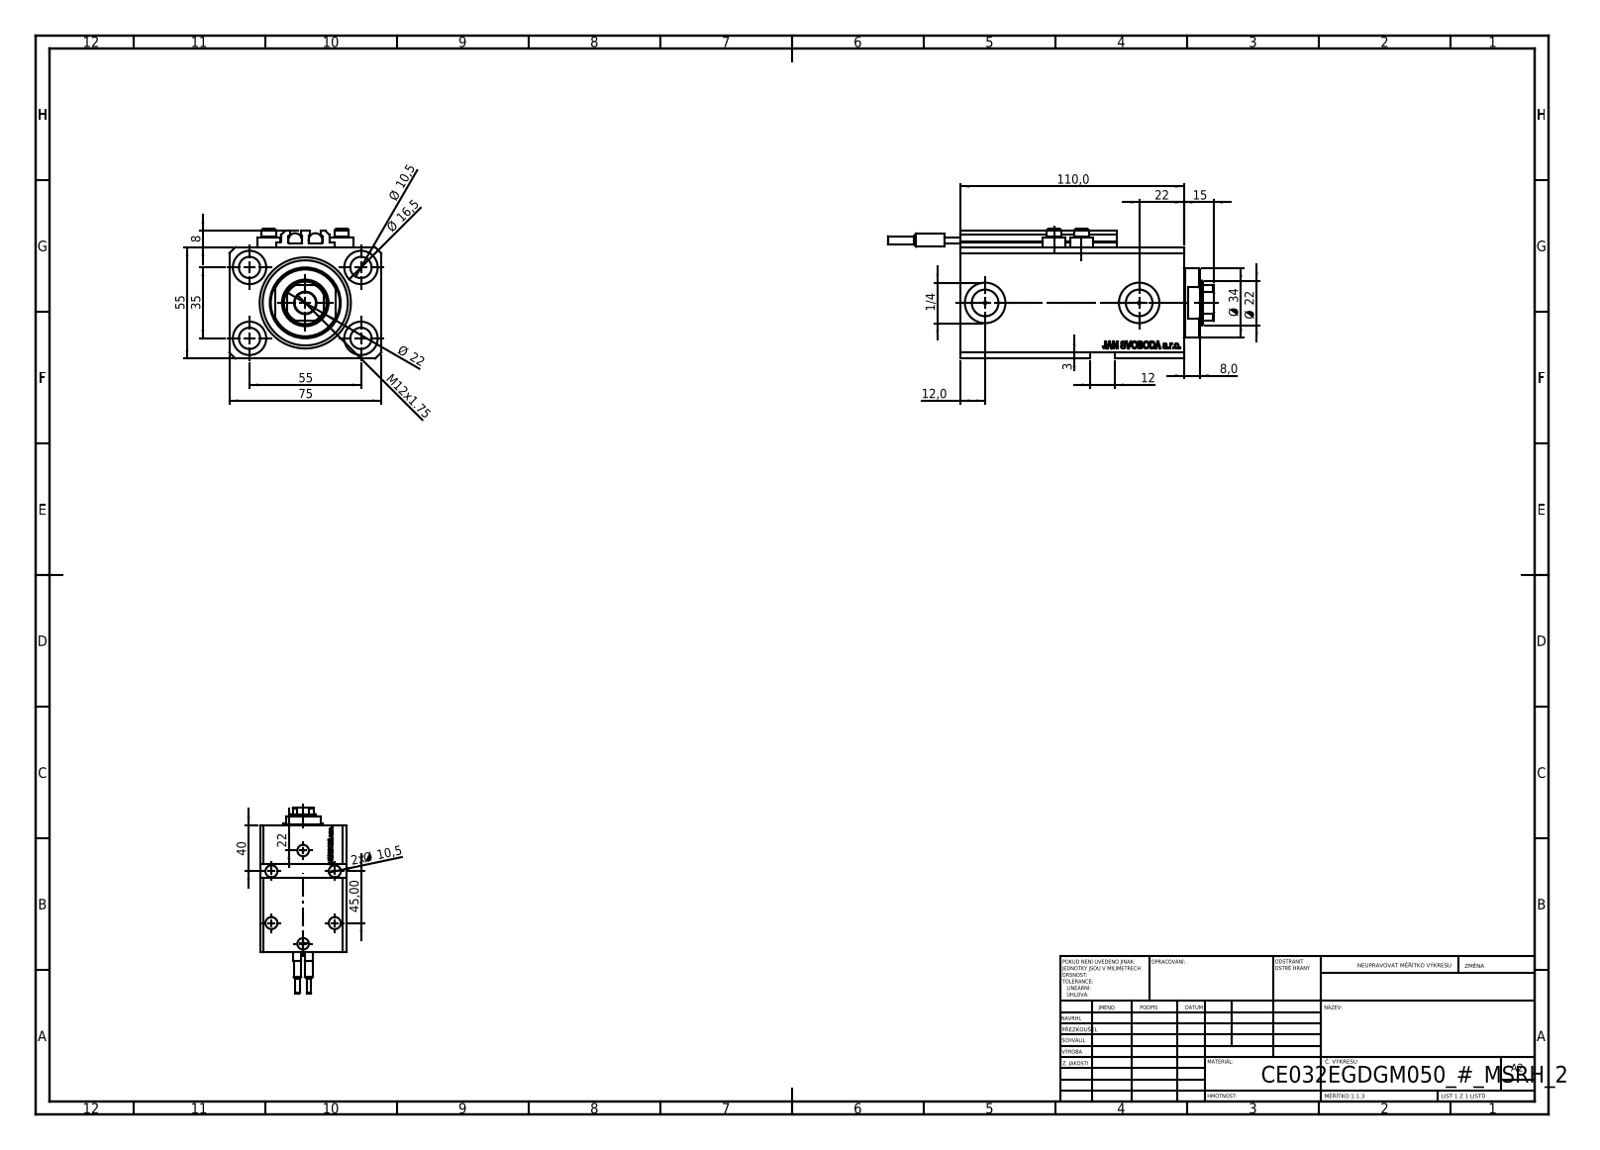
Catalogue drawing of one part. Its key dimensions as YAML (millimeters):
part_name: "SWITCH_V250CE; ALLEN BOLT V250CE; V250CE_C_VCP; V250CE_E_Body (+1 more)"
step_written_by: "SolidWorks 2019 (CONFIG_CONTROL_DESIGN)"
units: millimeters
bodies: {solids: 10, faces: 1152, planar: 550, cylindrical: 170, other: 432}
overall_size: [161, 75, 64]
volume: 381291
surface_area: 99541
round_holes:
  - {diameter: 10.5, count: 9}
  - {diameter: 1.25, count: 4}
  - {diameter: 4, count: 4}
  - {diameter: 16.5, count: 4}
  - {diameter: 10, count: 2}
  - {diameter: 13.16, count: 2}
  - {diameter: 20, count: 2}
  - {diameter: 22, count: 1}
  - {diameter: 32, count: 1}
  - {diameter: 45, count: 1}
round_bosses_or_shafts:
  - {diameter: 11.6, count: 4}
  - {diameter: 7, count: 4}
  - {diameter: 6.8, count: 2}
  - {diameter: 6.5, count: 2}
  - {diameter: 4, count: 2}
  - {diameter: 34, count: 1}
partial_cylinders:
  - {radius: 0.2, count: 10}
  - {radius: 10.5, count: 1}
face_to_face_distances: [55, 75, 3, 15, 110, 57, 95, 9.9, 85.1, 100.1]
hole_center_spacings: [32.6, 32.87, 55, 68.74, 13.6, 14.09, 23.05, 25.81]
